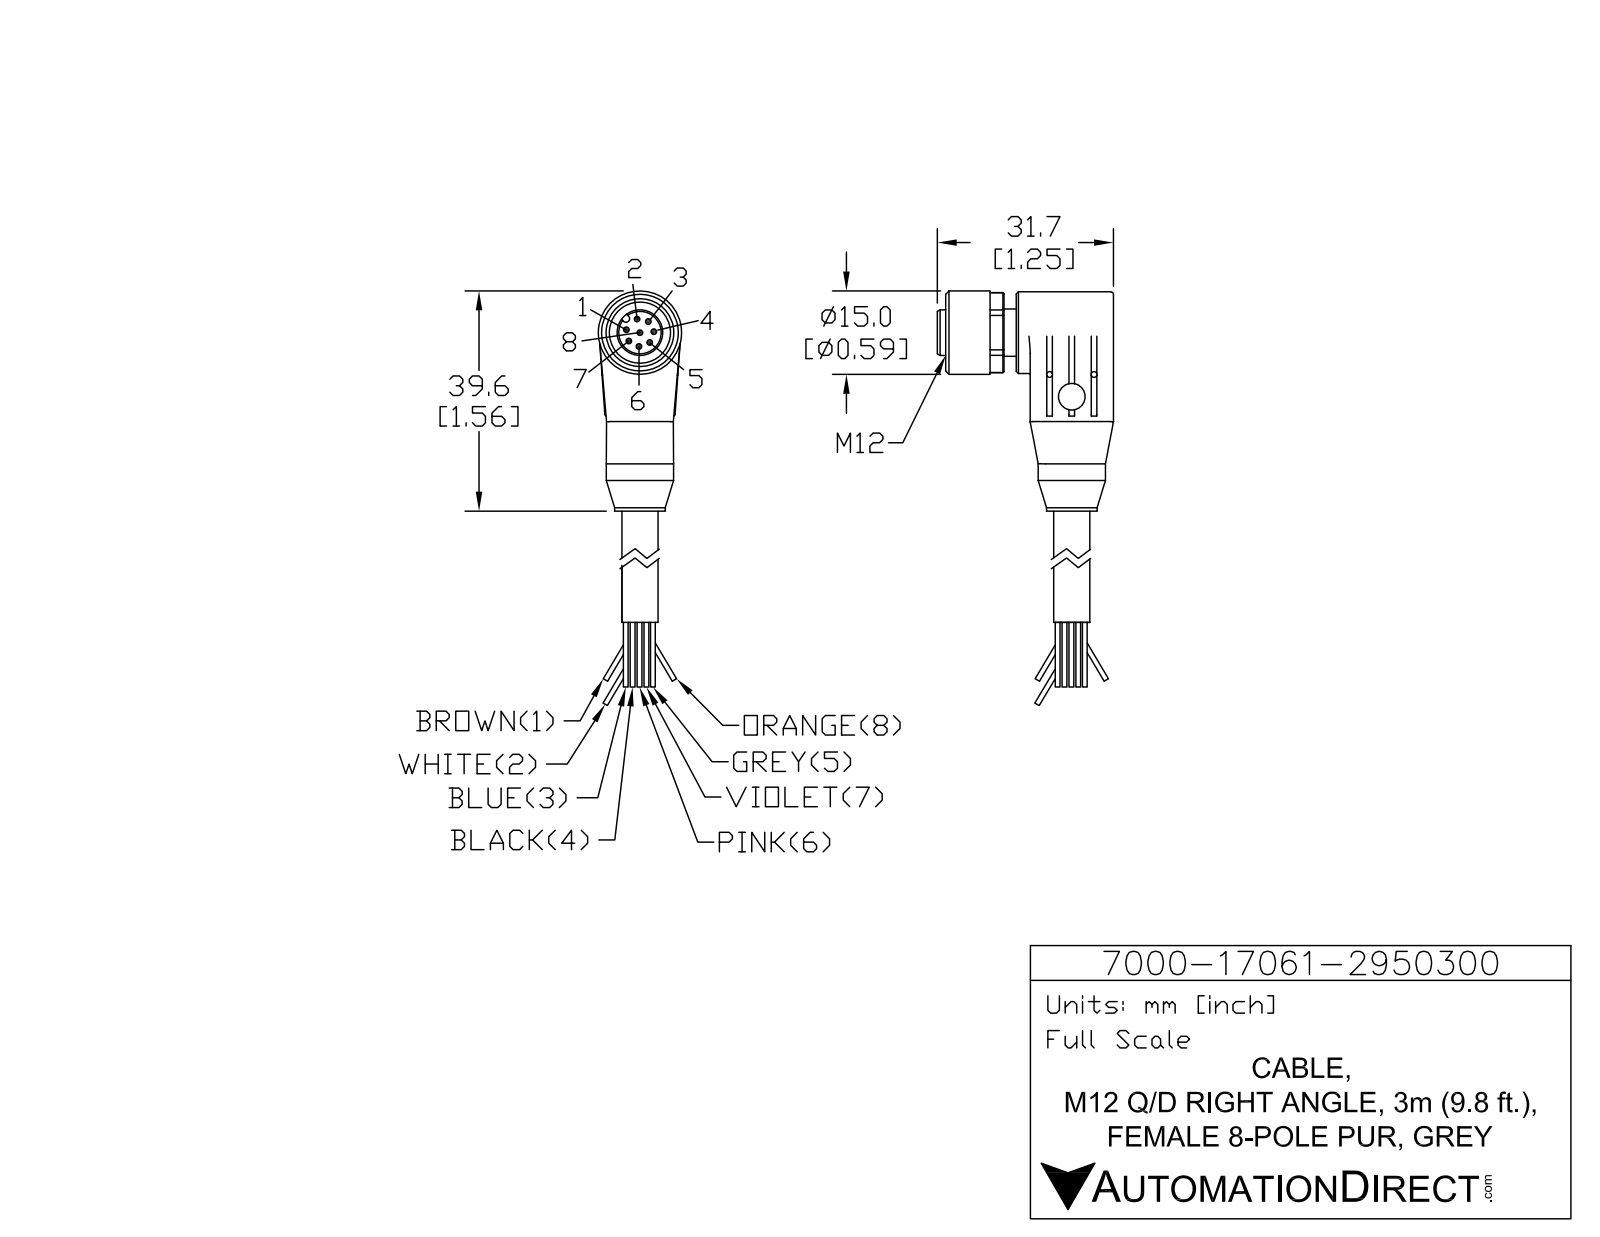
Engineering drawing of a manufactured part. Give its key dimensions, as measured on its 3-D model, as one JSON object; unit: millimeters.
{"part_name": "7000-17061-2950300", "step_written_by": "SolidWorks 2015 (AUTOMOTIVE_DESIGN)", "units": "millimeters", "bodies": {"solids": 1, "faces": 174, "planar": 73, "cylindrical": 67, "other": 34}, "overall_size": [59.6, 31.7, 15], "volume_mm3": 9094, "surface_area_mm2": 4084, "round_holes": [[1, 8], [1.05, 4], [4.8, 1], [11, 1]], "round_bosses_or_shafts": [[15, 1], [14.7, 1], [12.1, 1], [9.1, 1], [8.5, 1], [8.2, 1], [6.5, 1]], "partial_cylinders_radius": [[0.5, 4], [0.3, 2], [0.65, 1], [7.2, 1]], "face_to_face_distances": [2.5, 15, 4.7, 17.5, 19.7, 2.2, 3, 7.7, 12, 16.7], "hole_center_spacings": [2.5, 2.07, 3.78, 4.95, 2.08, 4.22, 4.79, 4.8]}
